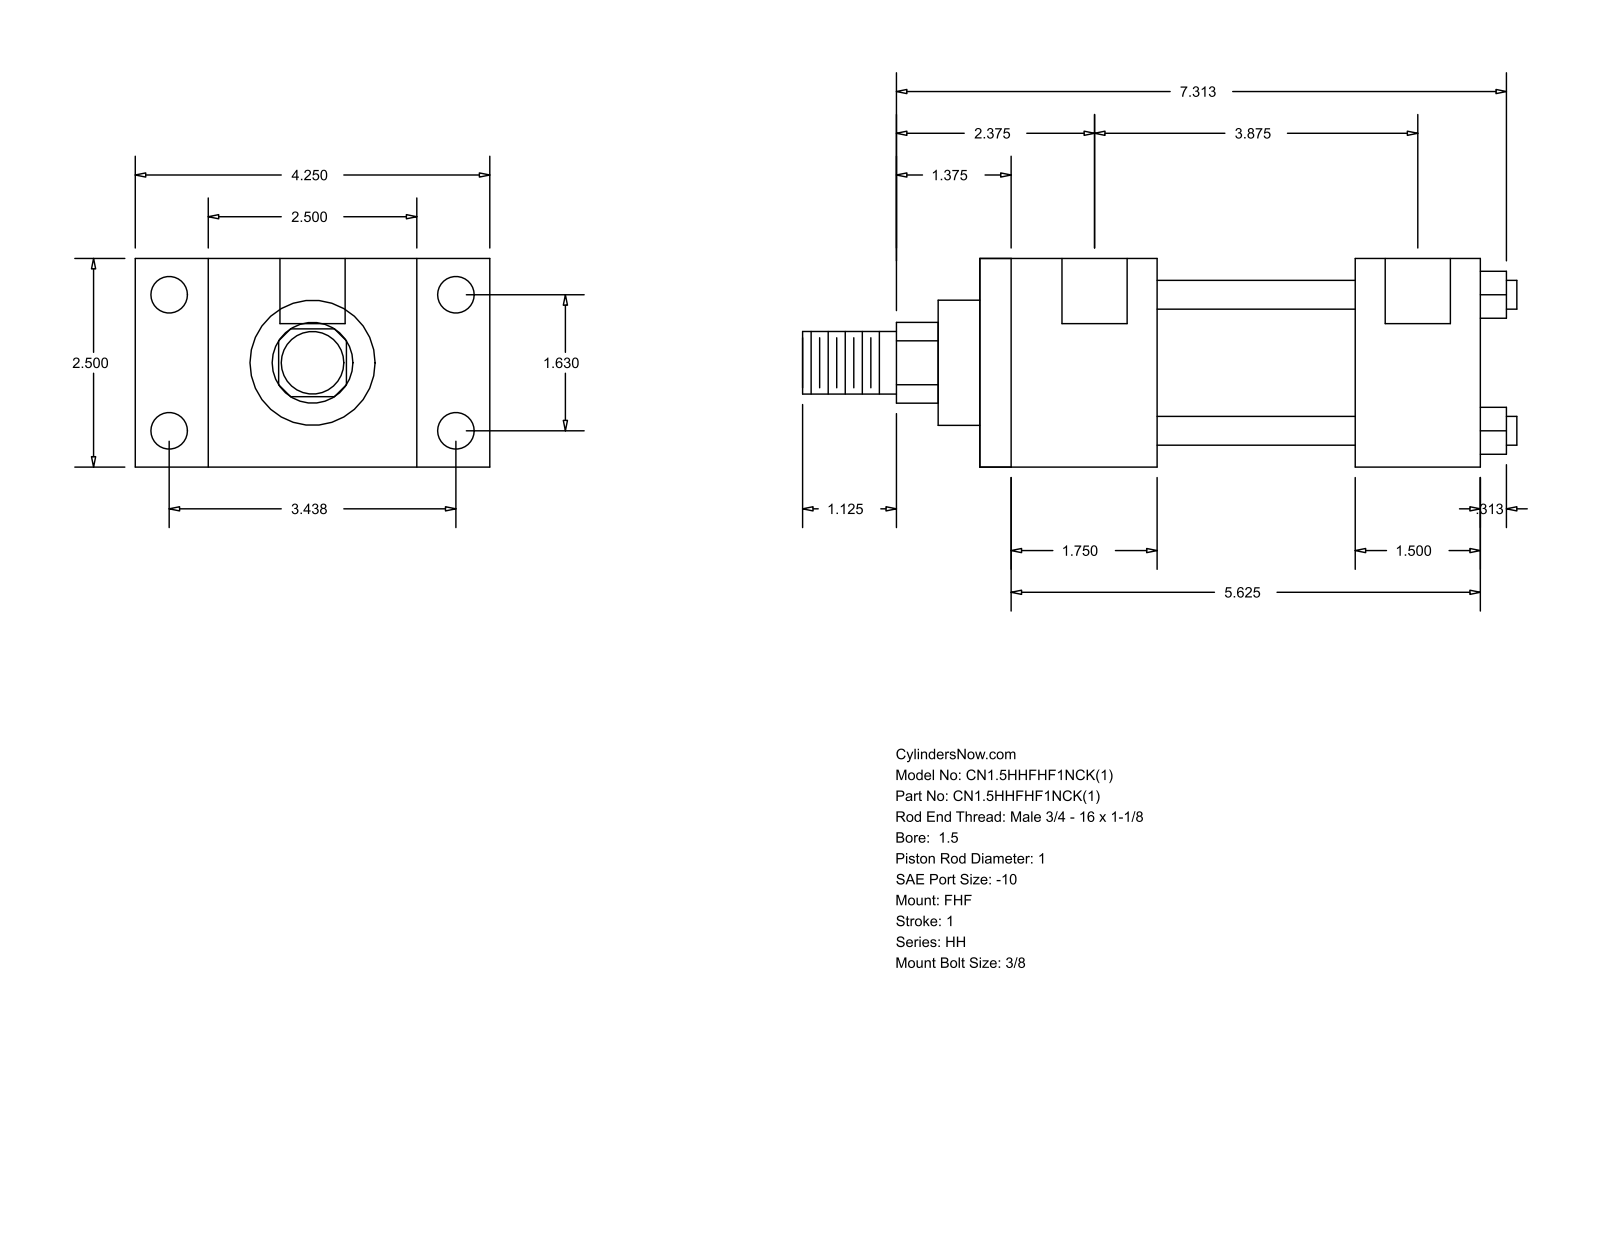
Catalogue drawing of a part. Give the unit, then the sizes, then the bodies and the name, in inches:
Units: inches
Overall size (bounding box): 8.563 × 4.25 × 2.5
Round holes (diameter × count): ⌀0.219 ×4, ⌀0.438 ×4, ⌀0.781 ×2
Round bosses / shafts (diameter × count): ⌀0.345 ×4, ⌀1.75 ×1, ⌀1.5 ×1, ⌀1 ×1, ⌀0.75 ×1
Partial cylindrical surfaces — rounded edges, fillets, slot ends (radius × count): R0.484 ×1
Main face-to-face distances: 2.5, 0.875, 3.375, 2.125, 4.25, 6, 3.875, 1.5, 4.5, 2.375
Hole centre spacings: 0.063, 1.63, 3.438, 3.805, 3.937, 4, 3.875
Bodies: 0 solids, 88 faces (60 planar, 28 cylindrical, 0 other)
Part name (STEP PRODUCT): HH_FHF__0150_1
STEP written by: GSSL Pune (CONFIG_CONTROL_DESIGN)
